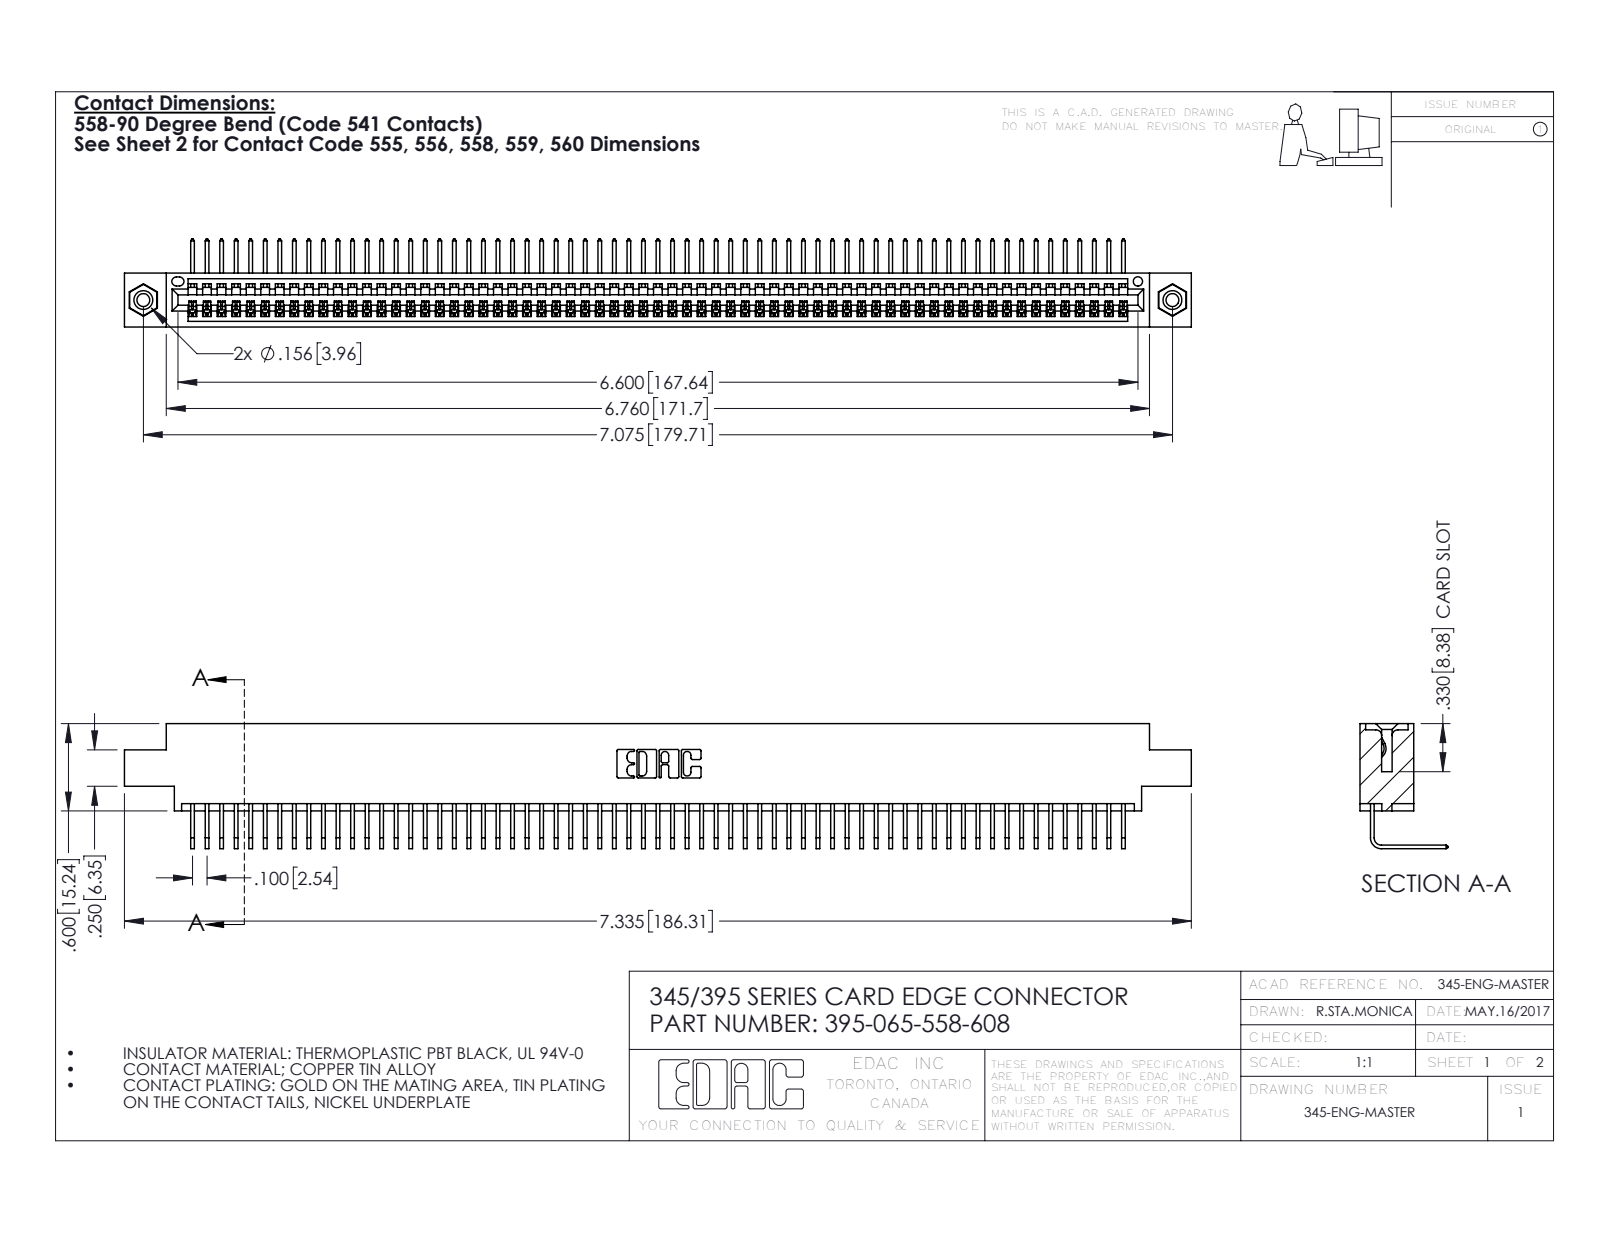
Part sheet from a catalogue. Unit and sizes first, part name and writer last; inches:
Units: inches
Overall size (bounding box): 7.335 × 0.859 × 0.605
Round holes (diameter × count): ⌀0.089 ×2, ⌀0.125 ×2, ⌀0.156 ×2, ⌀0.064 ×1
Round bosses / shafts (diameter × count): ⌀0.155 ×2
Partial cylindrical surfaces — rounded edges, fillets, slot ends (radius × count): R0.006 ×130, R0.01 ×22, R0.007 ×6, R0.031 ×6, R0.026 ×3, R0.031 ×2, R0.04 ×2, R0.014 ×1
Main face-to-face distances: 0.072, 0.298, 0.37, 0.2, 0.098, 0.272, 0.025, 0.225, 0.175, 0.149
Hole centre spacings: 0.27, 6.839, 7.075
Volume: 1.097 in³ · Surface area: 39.72 in²
Bodies: 68 solids, 4090 faces (2846 planar, 1228 cylindrical, 16 other)
Part name (STEP PRODUCT): 395-065-558-608; 345 Part_0.170 Offset - 0.156 Dia-TI; 345-250-001_345-250-003-102; 345-292-001_558 Tail - 2
STEP written by: SolidWorks 2016 (CONFIG_CONTROL_DESIGN)
